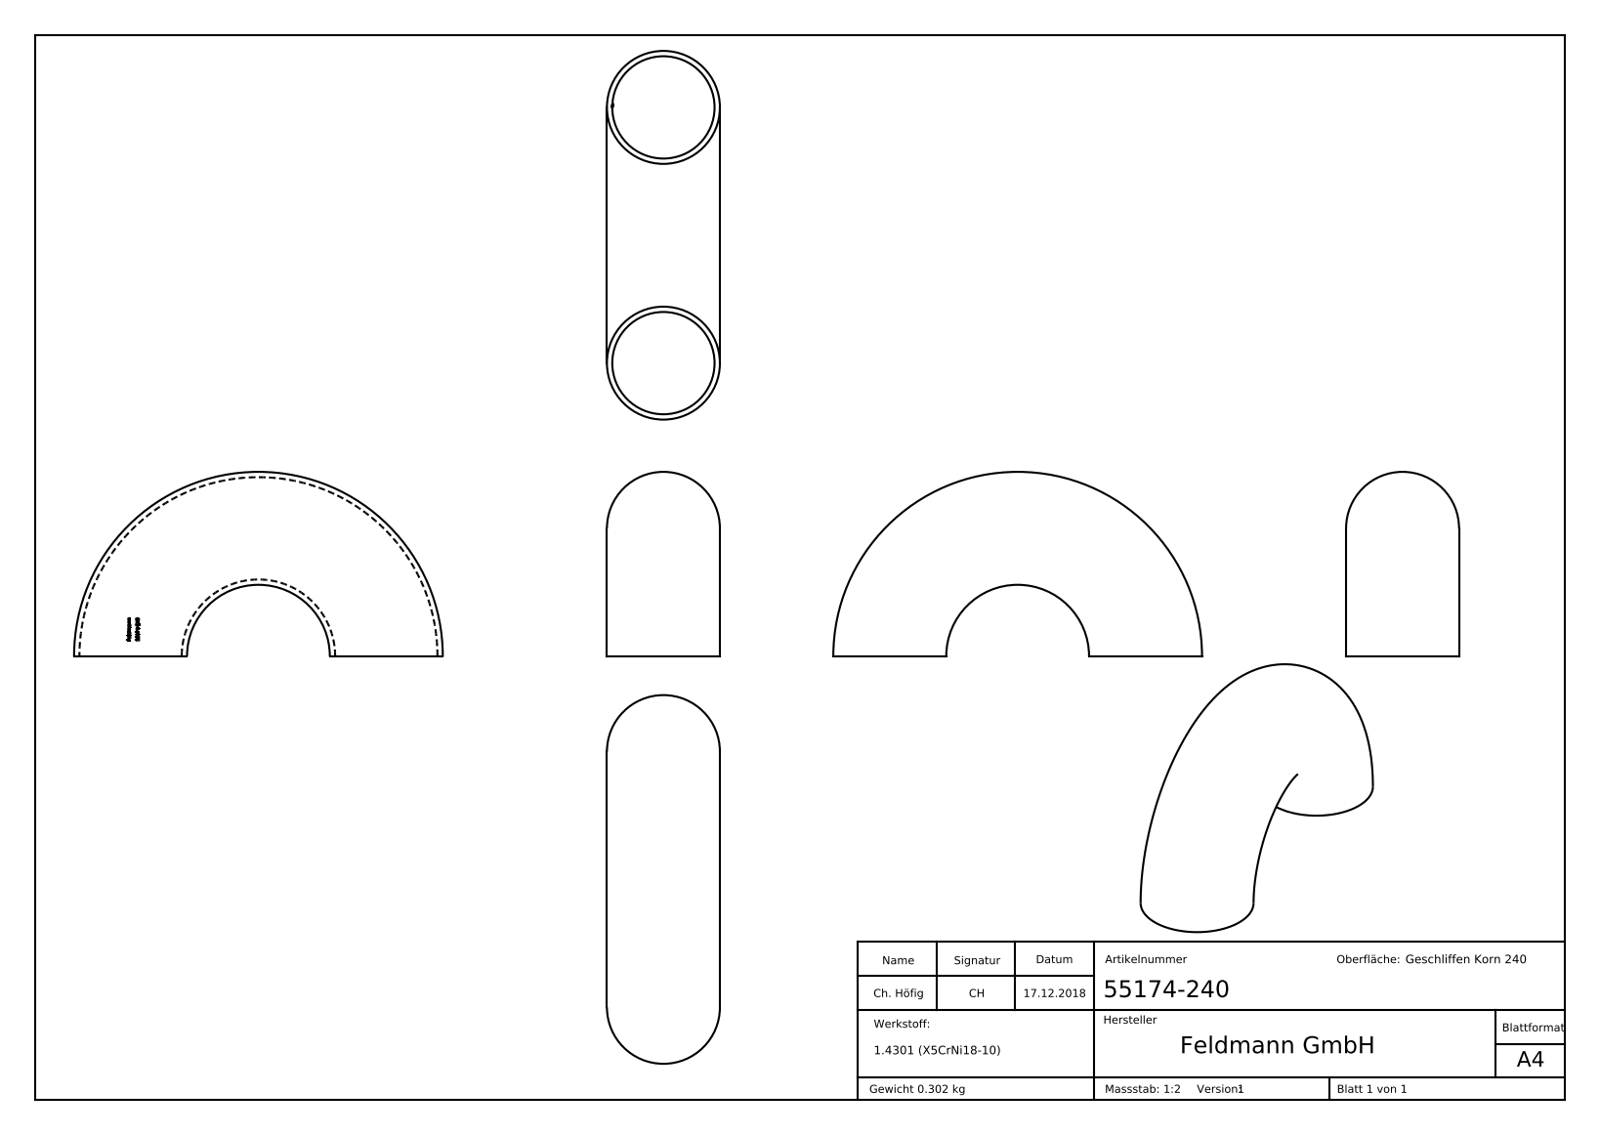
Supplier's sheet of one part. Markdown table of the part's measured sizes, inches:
| quantity | value |
| --- | --- |
| part name | 55174-240 |
| STEP written by | SolidWorks 2015 (CONFIG_CONTROL_DESIGN) |
| units | inches |
| bodies | 1 solid, 222 faces (116 planar, 0 cylindrical, 106 other) |
| overall size | 5.449 × 2.724 × 1.669 |
| volume | 2.336 in³ |
| surface area | 60.13 in² |
| main face-to-face distances | 0.015, 0.05, 0.035, 0.167, 0.039, 0.104, 0.133, 0.018, 0.129, 0.034 |
